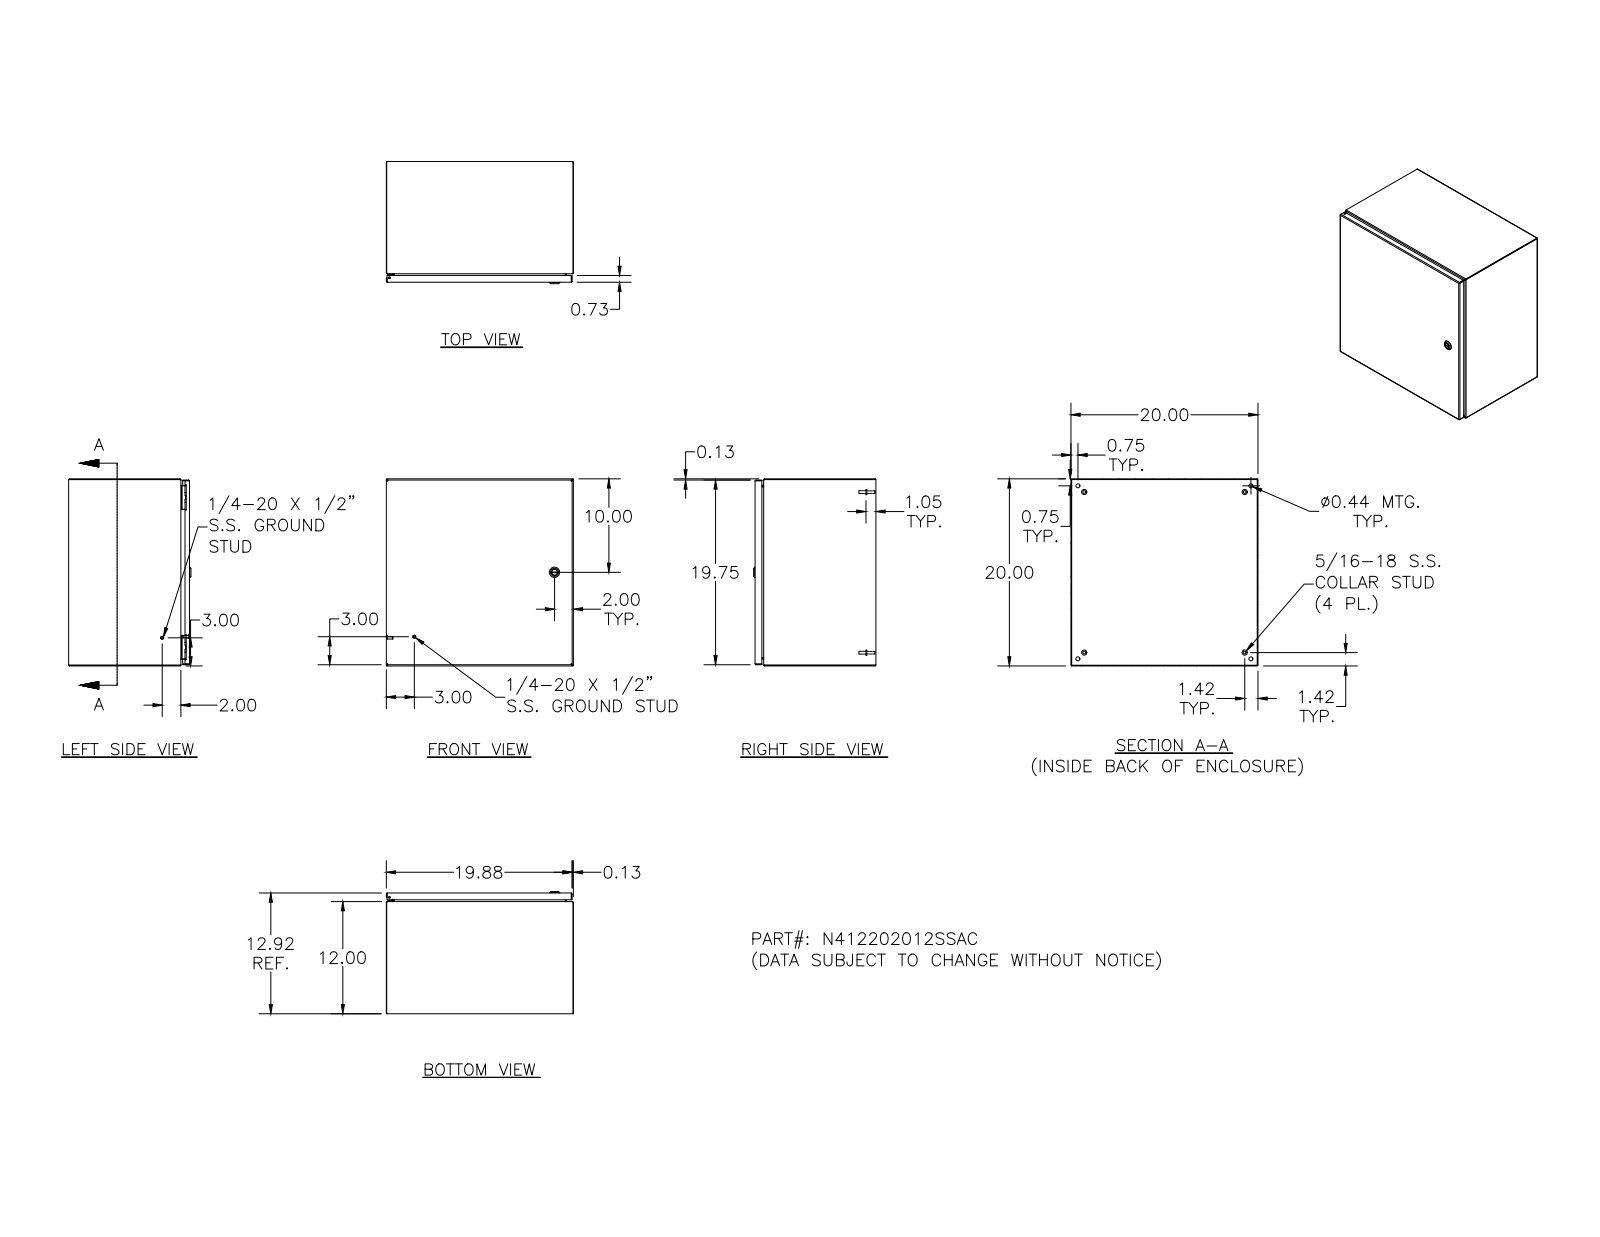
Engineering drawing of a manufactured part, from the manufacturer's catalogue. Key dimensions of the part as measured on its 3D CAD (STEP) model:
Part name (STEP PRODUCT): N412202012SSAC; N412202012SSACBKP; 388151; N4122020SSACLID (+8 more)
STEP written by: Autodesk Inventor 2011 (AUTOMOTIVE_DESIGN)
Units: inches
Bodies: 34 solids, 1364 faces (523 planar, 497 cylindrical, 344 other)
Overall size (bounding box): 20 × 20 × 13.075
Volume: 142.3 in³ · Surface area: 3 866 in²
Round holes (diameter × count): ⌀0.188 ×5, ⌀0.093 ×4, ⌀0.152 ×4, ⌀0.167 ×4, ⌀0.172 ×4, ⌀0.437 ×4, ⌀0.156 ×2, ⌀0.187 ×1, ⌀0.197 ×1, ⌀0.315 ×1, ⌀0.394 ×1, ⌀0.402 ×1
Round bosses / shafts (diameter × count): ⌀0.25 ×10, ⌀0.563 ×4, ⌀0.36 ×4, ⌀0.32 ×4, ⌀0.3 ×4, ⌀0.275 ×4, ⌀0.256 ×4, ⌀0.164 ×4
Partial cylindrical surfaces — rounded edges, fillets, slot ends (radius × count): R0.05 ×26, R0.016 ×18, R0.016 ×16, R0.09 ×16, R0.031 ×14, R0.125 ×14, R0.02 ×9, R0.032 ×8
Main face-to-face distances: 0.074, 19.926, 12.843, 20, 19.852, 12.769, 12.917, 11.926, 0.917, 0.739
Hole centre spacings: 16, 0.017, 0.66, 16.008, 18.5, 18.872, 0.019, 0.5
